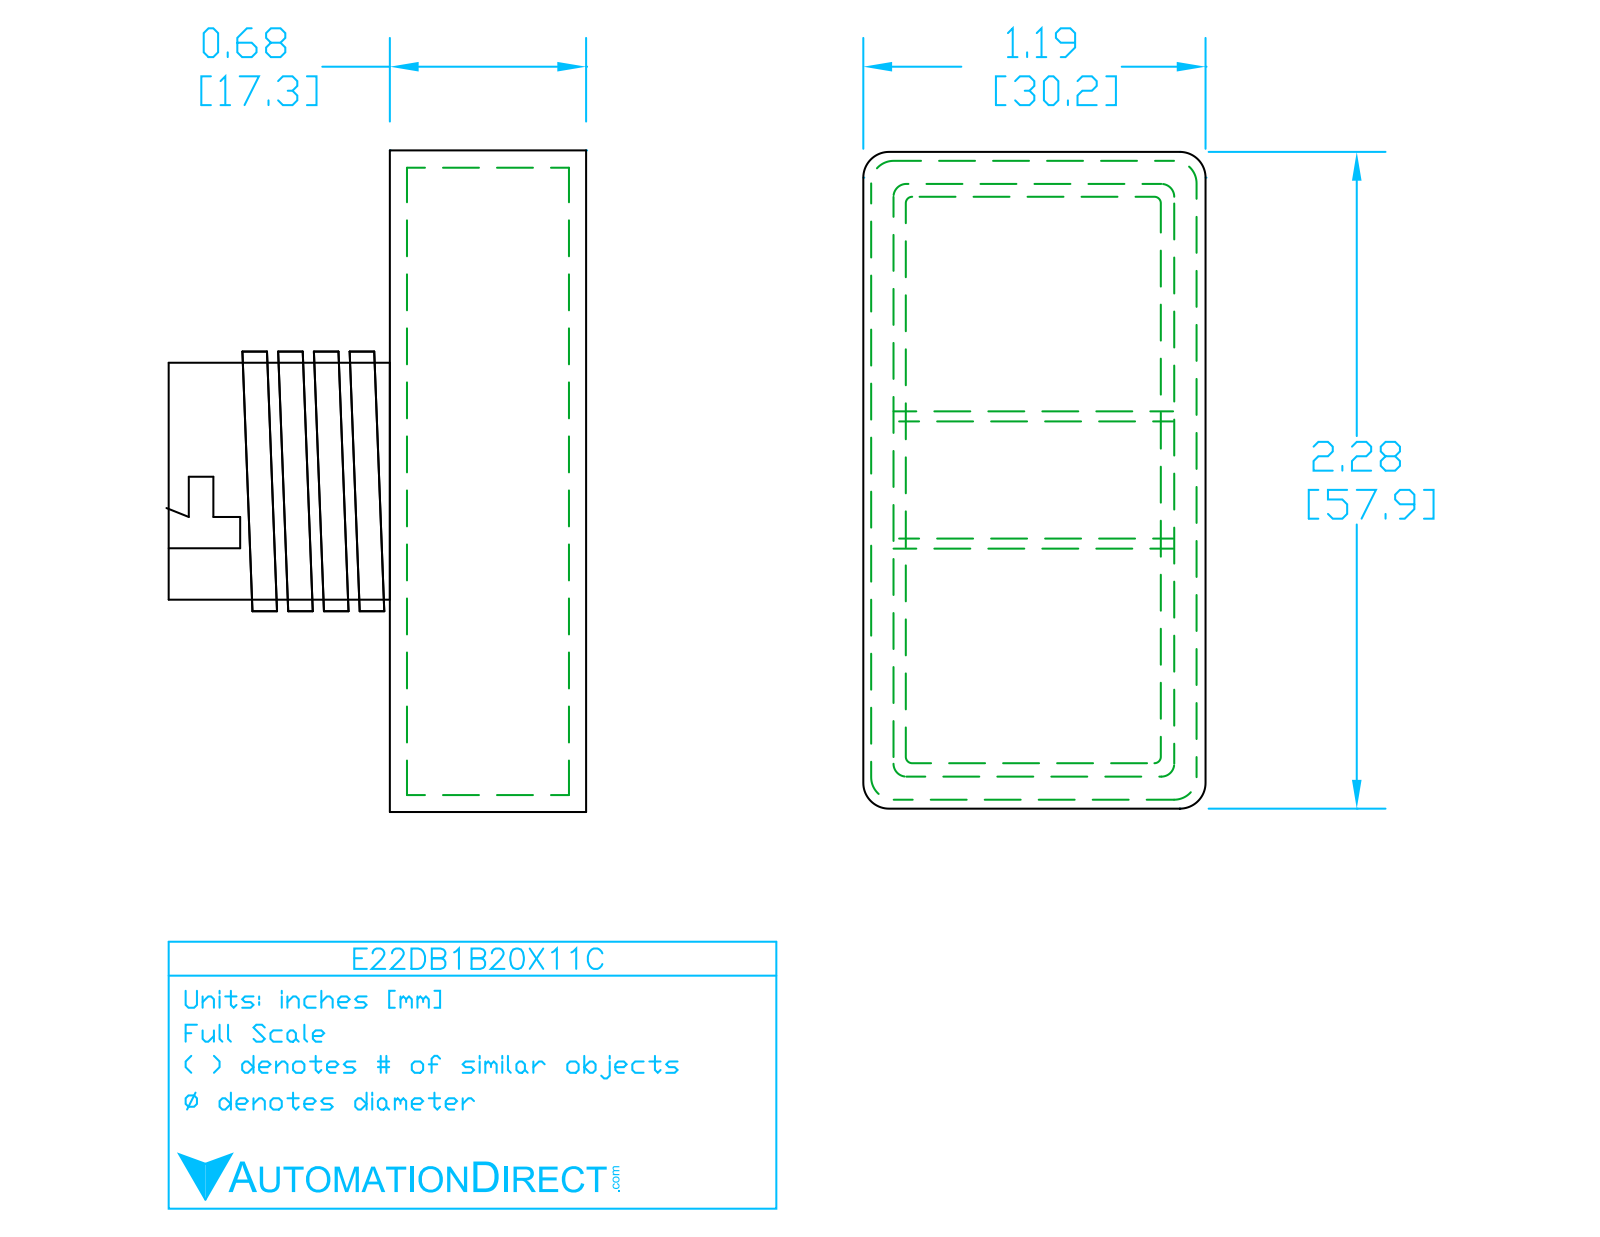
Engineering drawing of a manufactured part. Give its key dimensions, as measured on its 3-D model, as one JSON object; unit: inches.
{"part_name": "E22TB3X4B", "step_written_by": "SolidWorks 2017 (AUTOMOTIVE_DESIGN)", "units": "inches", "bodies": {"solids": 8, "faces": 263, "planar": 217, "cylindrical": 44, "other": 2}, "overall_size": [2.689, 1.885, 1.171], "volume_in3": 2.526, "surface_area_in2": 32.5, "round_holes": [[0.236, 4], [0.827, 1], [0.866, 1], [1.014, 1]], "round_bosses_or_shafts": [[1.161, 1], [1.142, 1], [1.102, 1], [1.063, 1], [0.984, 1], [0.945, 1]], "partial_cylinders_radius": [[0.055, 2], [0.118, 2], [0.482, 1]], "face_to_face_distances": [0.394, 0.787, 1.043, 0.315, 0.079, 0.728, 0.039, 0.335, 1.22, 0.236], "hole_center_spacings": [0.394, 0.557, 0.787, 0.88]}
